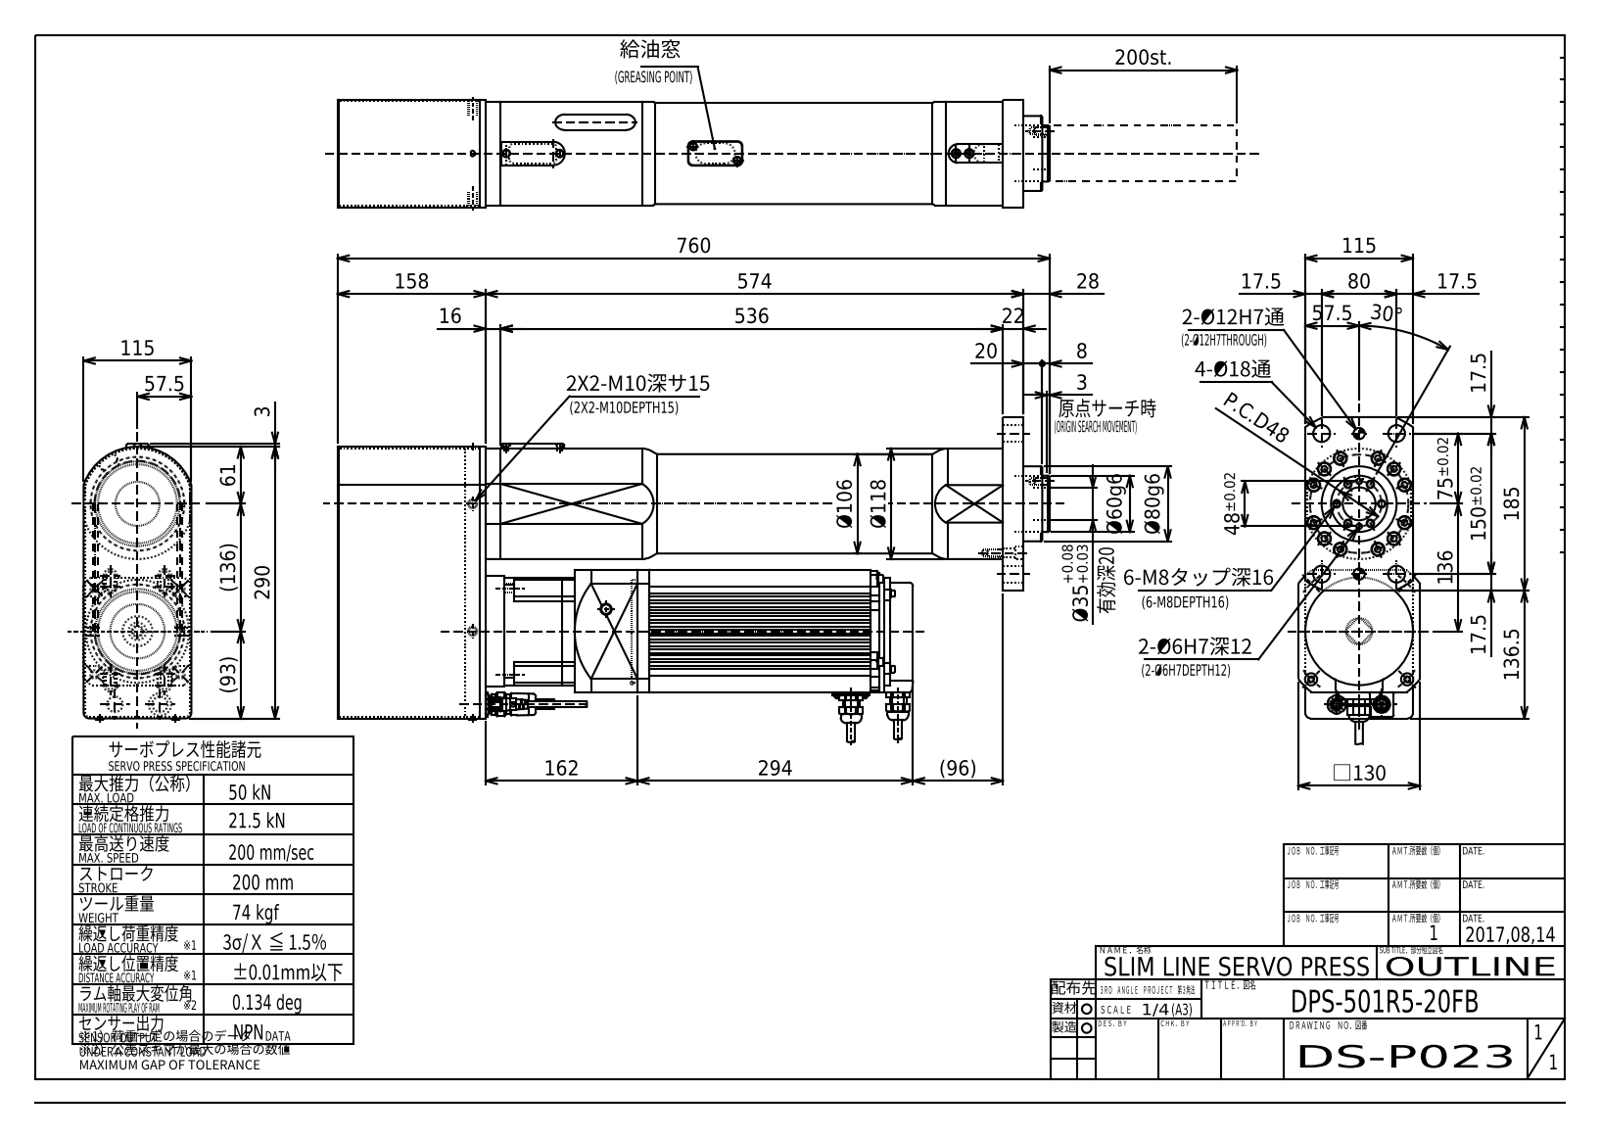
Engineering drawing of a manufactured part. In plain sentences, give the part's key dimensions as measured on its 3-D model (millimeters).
The part is named "DPS-501R5-20FB(DS-P023+B)_OUTLINE_20220414". Its 3-D file was written by "Autodesk Inventor 2021 (AUTOMOTIVE_DESIGN)". It is 2 solids with 1723 faces: 999 planar, 474 cylindrical and 250 other. Overall it measures 760 by 345.51 by 130 millimeters. Its volume is 17 000 000 cubic millimeters and its surface area 850 281 square millimeters. Round holes: 20 of diameter 6.65, 16 of diameter 9, 12 of diameter 14, 5 of diameter 11, 4 of diameter 6.75, 4 of diameter 8.2, 4 of diameter 18, 3 of diameter 6, 2 of diameter 3.24, 2 of diameter 4.5, 2 of diameter 8, 2 of diameter 9.5. Round bosses or shafts: 25 of diameter 1, 20 of diameter 13, 11 of diameter 8, 9 of diameter 4, 6 of diameter 8.5, 4 of diameter 15.4, 4 of diameter 6, 3 of diameter 18. Partial cylindrical surfaces (rounded edges, fillets, slot ends): 40 of radius 5, 17 of radius 2, 14 of radius 1, 12 of radius 4.25, 11 of radius 4, 7 of radius 2.5, 5 of radius 10, 4 of radius 3. The main face-to-face distances are 3, 6, 9, 115, 65, 68, 71, 62, 24, 74. The hole center spacings are 24, 52.5, 31.68, 48.66, 65.55, 74.24, 75.23, 12.42.
